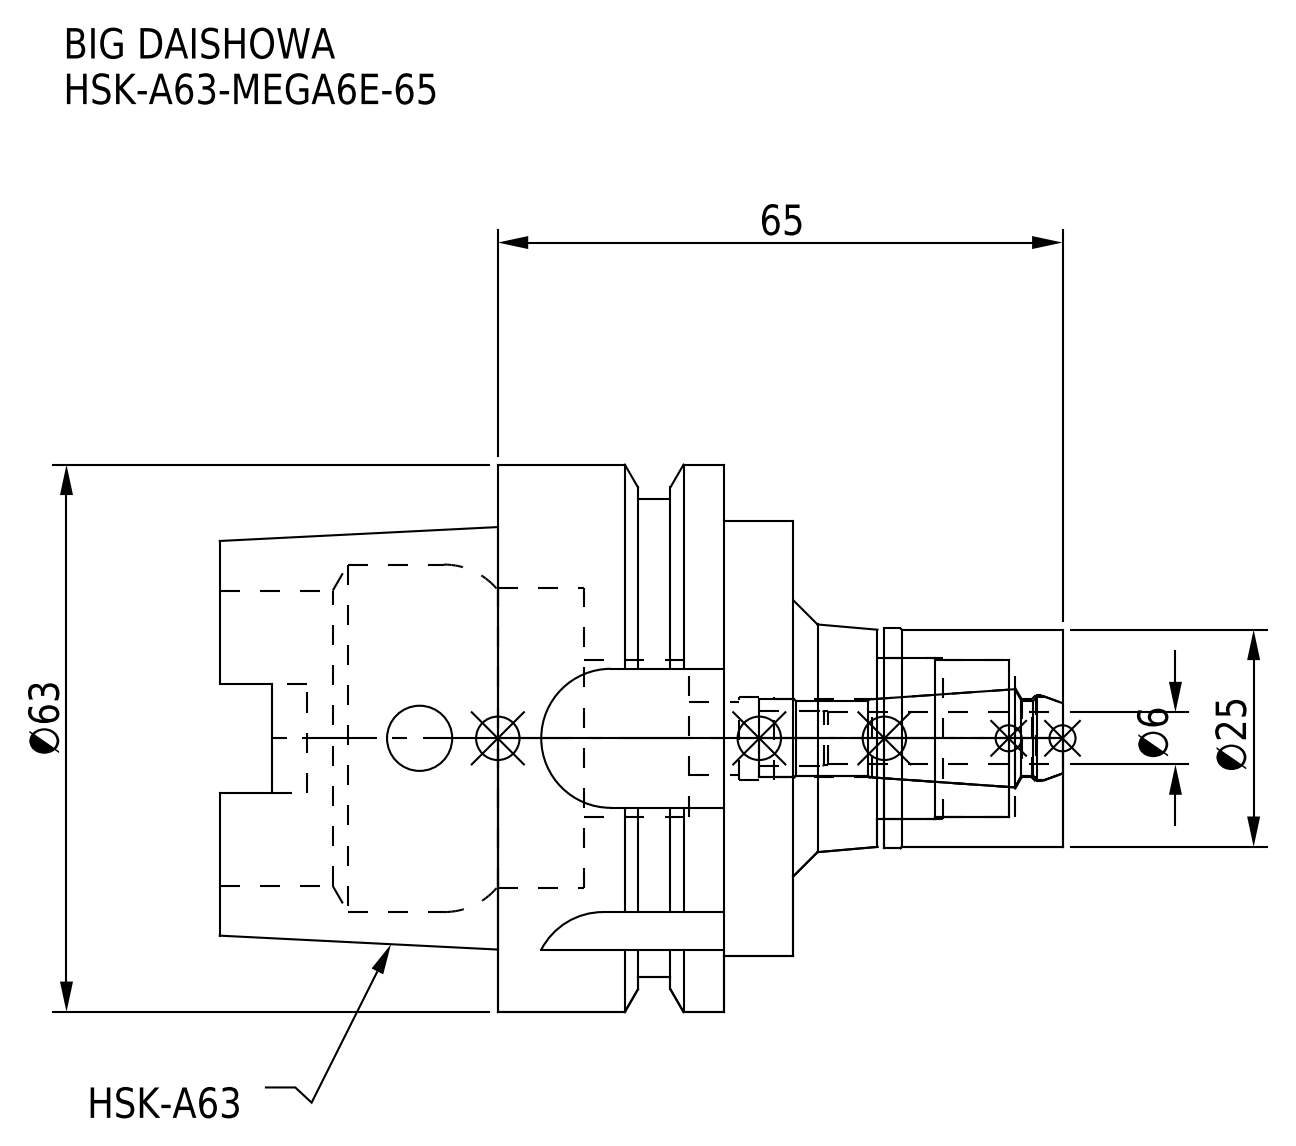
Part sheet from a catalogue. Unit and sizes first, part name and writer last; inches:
Units: inches
Overall size (bounding box): 3.819 × 2.48 × 2.48
Round holes (diameter × count): ⌀0.295 ×1, ⌀0.33 ×1, ⌀0.331 ×1, ⌀0.354 ×1, ⌀0.378 ×1, ⌀0.39 ×1, ⌀0.709 ×1, ⌀0.728 ×1, ⌀1.339 ×1, ⌀1.358 ×1, ⌀1.575 ×1
Round bosses / shafts (diameter × count): ⌀2.48 ×1, ⌀2.165 ×1, ⌀1.969 ×1, ⌀0.996 ×1, ⌀0.984 ×1
Partial cylindrical surfaces — rounded edges, fillets, slot ends (radius × count): R0.11 ×2, R0.113 ×2, R0.315 ×2, R0.354 ×1
Main face-to-face distances: 1.339, 1.024, 0.315, 0.947, 0.632, 0.392, 1.22, 1.535, 2.167, 2.559
Volume: 6.724 in³ · Surface area: 45.77 in²
Bodies: 2 solids, 126 faces (44 planar, 54 cylindrical, 28 other)
Part name (STEP PRODUCT): MEN6_1.stp; HSK-A63-MEGA6E-65-060-FreeParts; HSK-A63-MEGA6E-65; HSK-A63-MEGA6E-65_1.stp (+3 more)
STEP written by: SolidWorks 2019 (CONFIG_CONTROL_DESIGN)
